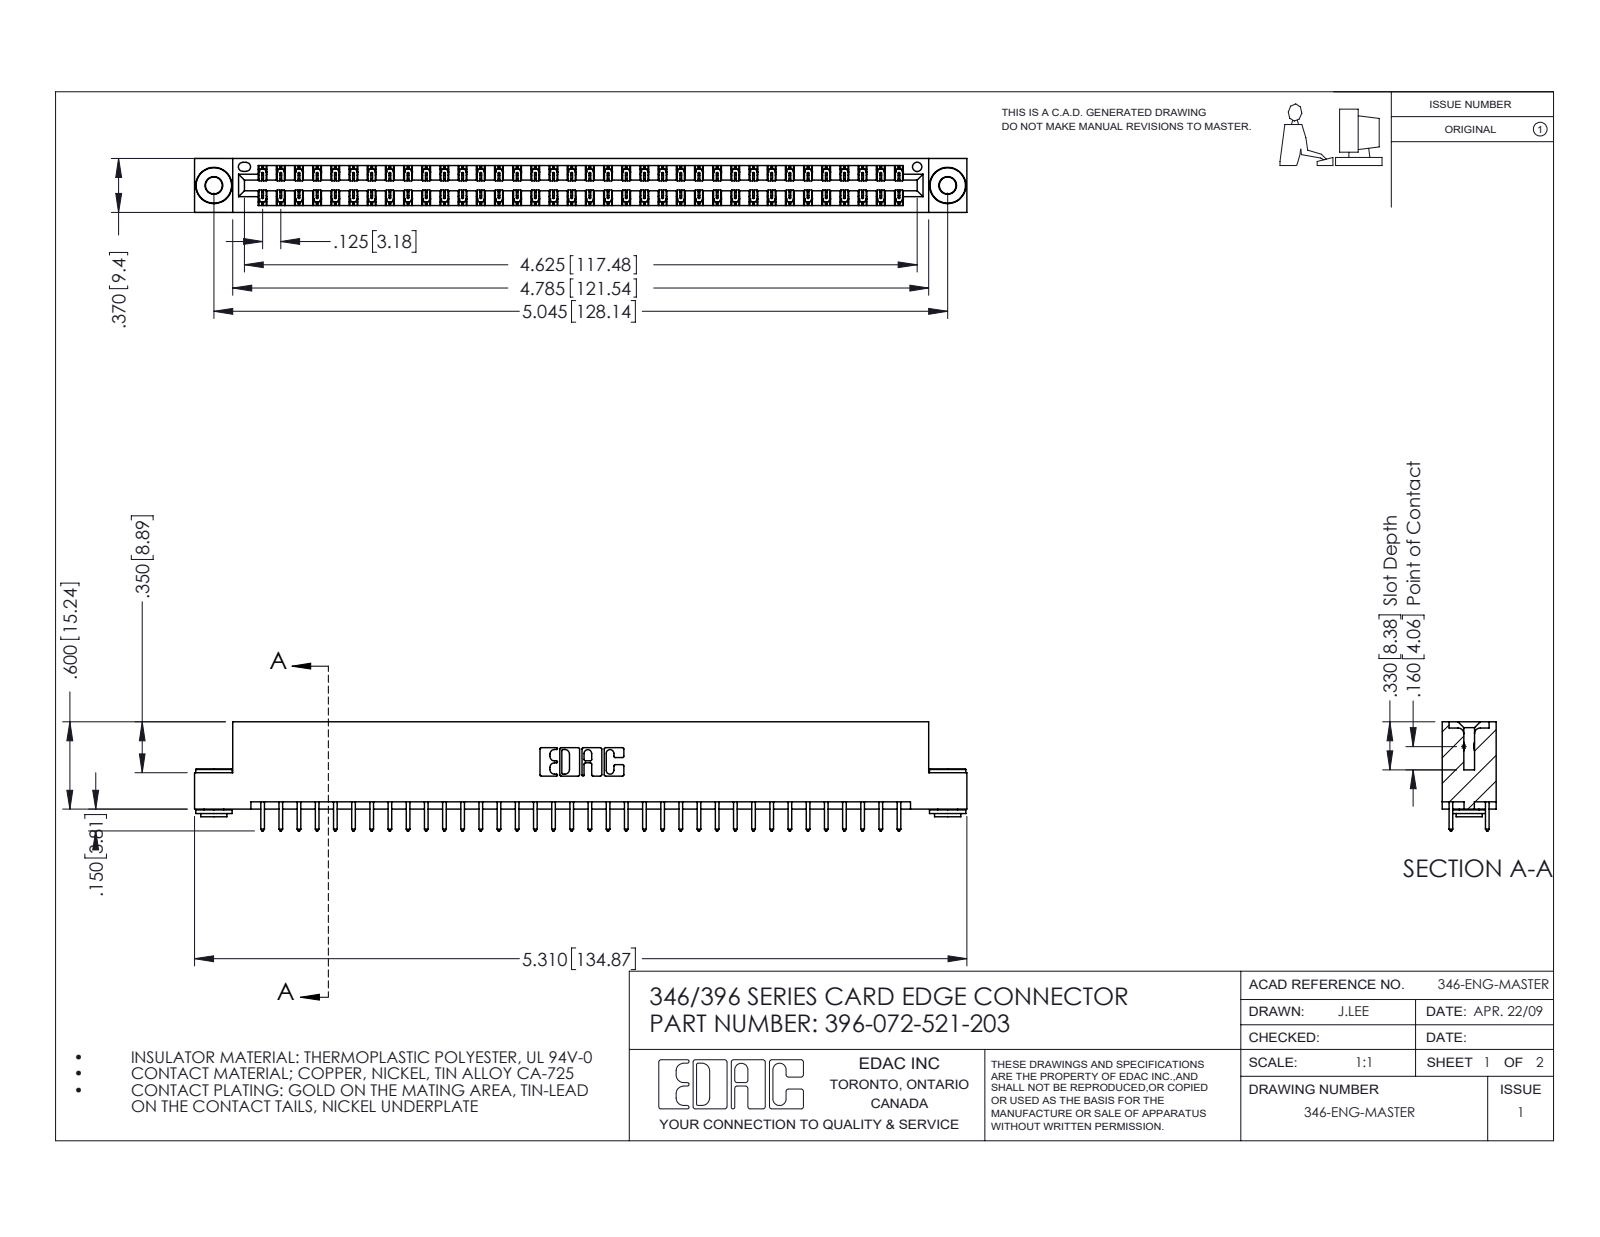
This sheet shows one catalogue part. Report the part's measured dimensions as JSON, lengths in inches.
{"part_name": "346 Part_Flush Mounting Lugs - 0.156 Dia-TH; 345-292-001_345-293-121; 345-250-002_345-250-002-102; 396-072-521-203", "step_written_by": "SolidWorks 2016 (CONFIG_CONTROL_DESIGN)", "units": "inches", "bodies": {"solids": 75, "faces": 3904, "planar": 2606, "cylindrical": 1290, "other": 8}, "overall_size": [5.31, 0.75, 0.37], "volume_in3": 0.799, "surface_area_in2": 27.78, "round_holes": [[0.116, 2], [0.156, 2], [0.064, 1]], "round_bosses_or_shafts": [[0.25, 2], [0.18, 2], [0.136, 2]], "partial_cylinders_radius": [[0.006, 108], [0.01, 72], [0.01, 22], [0.007, 6], [0.031, 6], [0.026, 3], [0.014, 2], [0.022, 2]], "face_to_face_distances": [0.048, 0.322, 0.25, 0.37, 0.025, 0.072, 0.298, 0.275, 0.148, 0.222], "hole_center_spacings": [0.246, 4.836, 5.045]}
